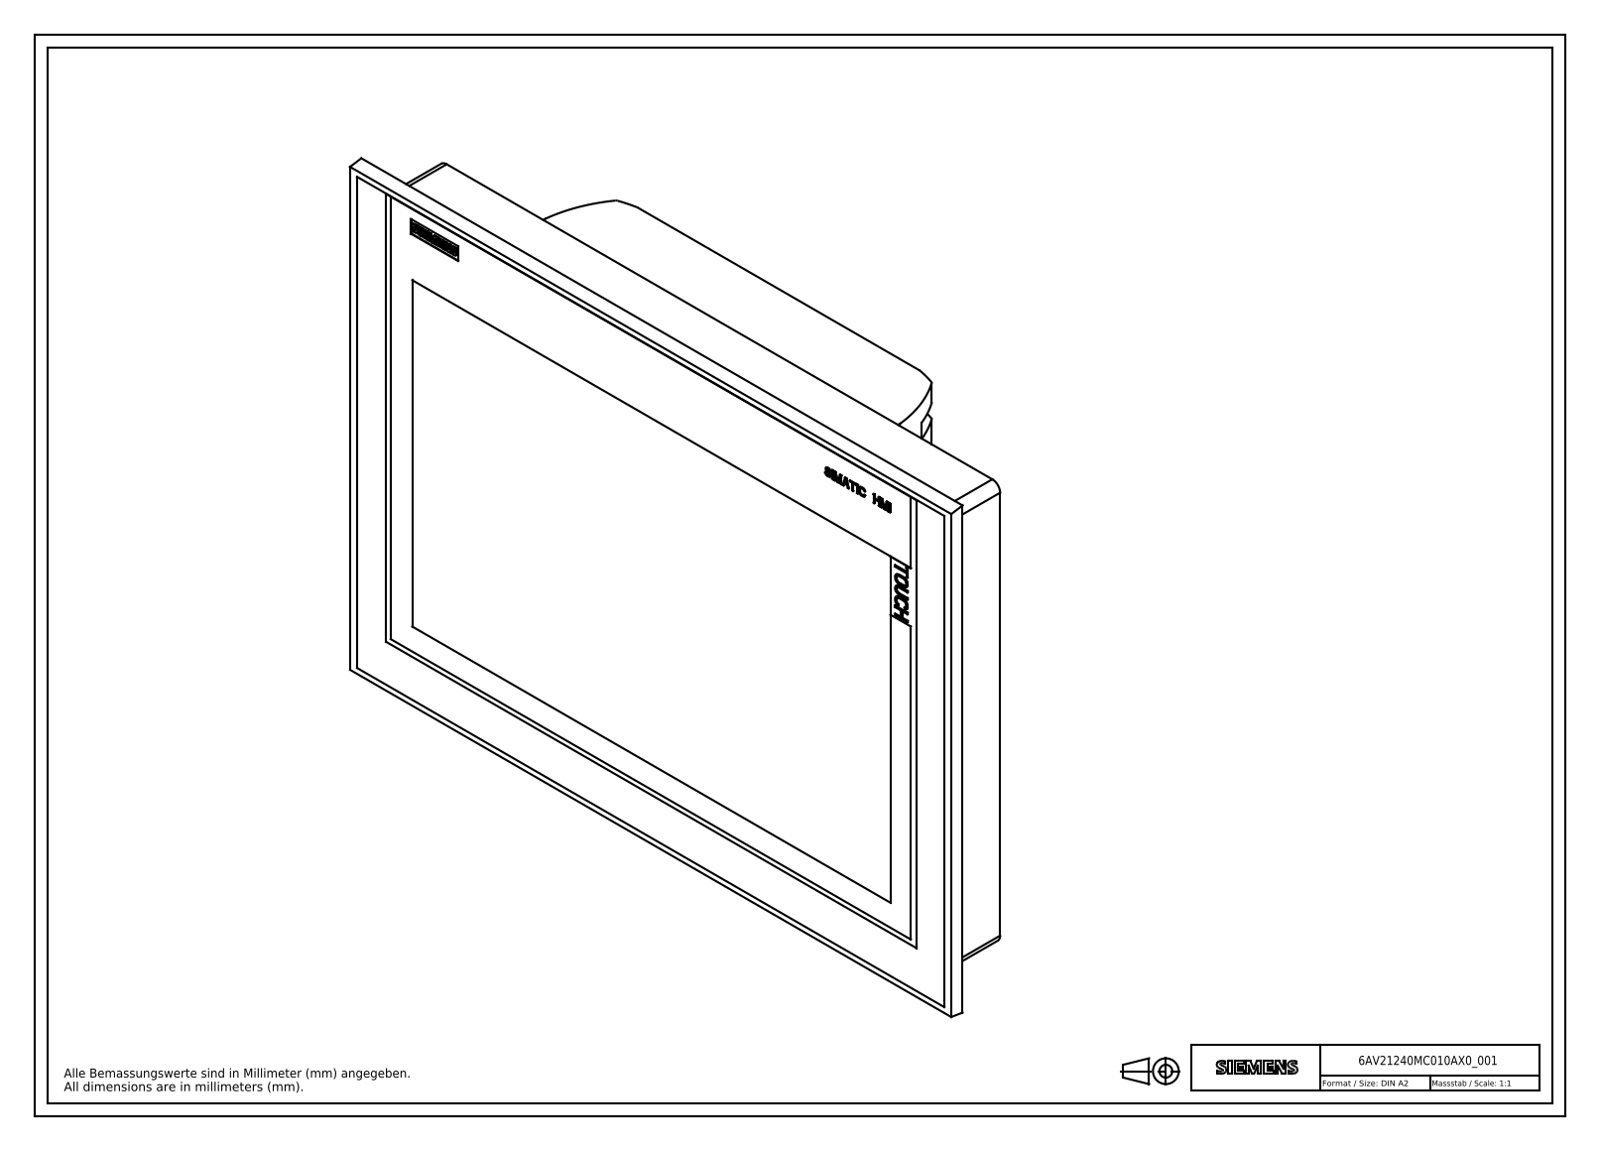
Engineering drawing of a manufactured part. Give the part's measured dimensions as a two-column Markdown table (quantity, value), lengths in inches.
| quantity | value |
| --- | --- |
| part name | A5E30321192A_001; A5E30291795A_001; A5E30291798A_001; A5E30291793A_001 (+1 more) |
| STEP written by | SIEMENS UGS NX 6.0 (AUTOMOTIVE_DESIGN) |
| units | inches |
| bodies | 270 solids, 3048 faces (2472 planar, 275 cylindrical, 301 other) |
| overall size | 12.992 × 9.488 × 2.768 |
| volume | 191.2 in³ |
| surface area | 430.2 in² |
| round holes (diameter × count) | 0.035 × 9, 0.094 × 2, 0.15 × 2, 0.335 × 2 |
| round bosses / shafts (diameter × count) | 0.217 × 9, 0.276 × 6, 0.118 × 2, 0.038 × 2, 0.031 × 2, 0.315 × 1 |
| partial cylindrical surfaces (radius × count) | 0.008 × 108, 0.012 × 24, 0.031 × 24, 0.029 × 16, 0.033 × 6, 0.059 × 6, 0.018 × 4, 0.02 × 4 |
| main face-to-face distances | 1.445, 1.276, 2.721, 2.747, 1.471, 0.026, 1.819, 0.543, 0.902, 0.928 |
| hole center spacings | 0.121, 0.109, 0.195, 0.217, 0.292, 0.326, 0.28, 0.333 |
